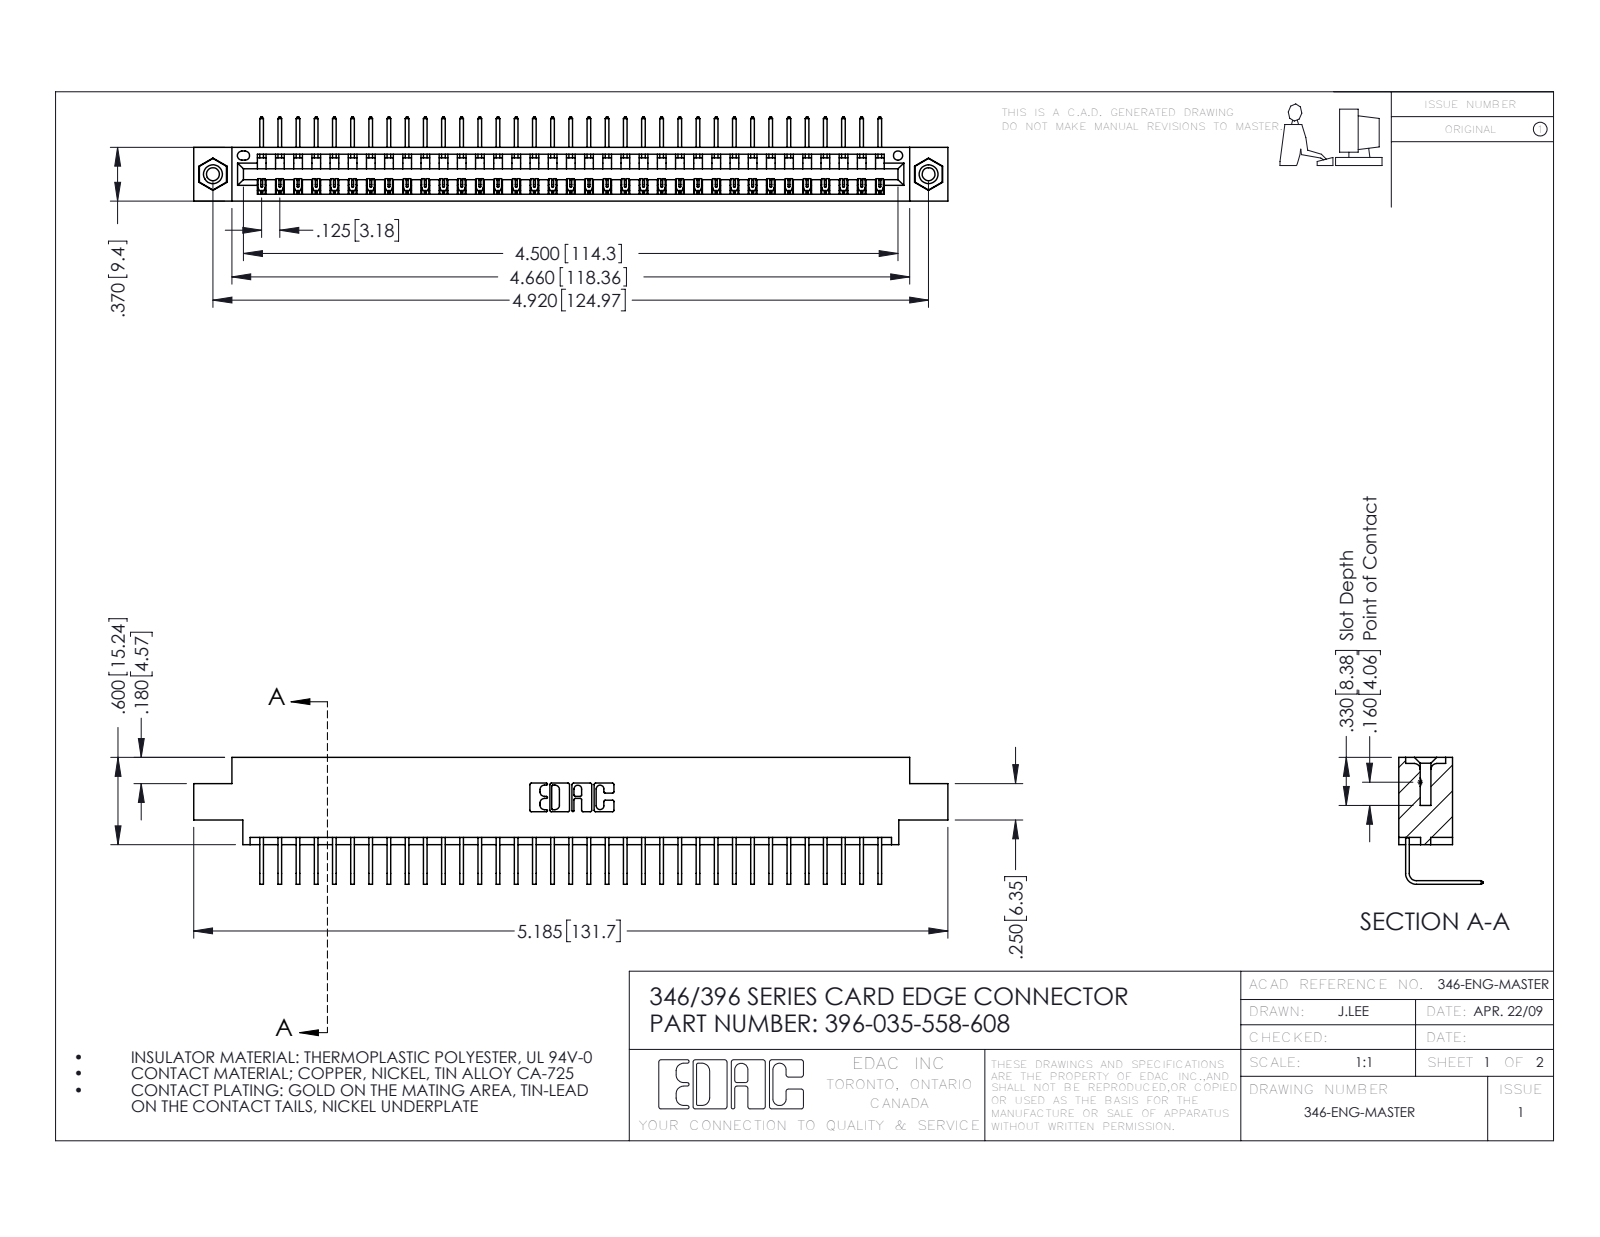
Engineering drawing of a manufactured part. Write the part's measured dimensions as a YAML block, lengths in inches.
part_name: "345-250-001_345-250-003-102; 396-035-558-608; 346 Part_0.170 Offset - 0.156 Dia-TI; 345-292-001_558 Tail - 2"
step_written_by: "SolidWorks 2016 (CONFIG_CONTROL_DESIGN)"
units: inches
bodies: {solids: 38, faces: 2286, planar: 1582, cylindrical: 688, other: 16}
overall_size: [5.185, 0.873, 0.58]
volume: 0.764
surface_area: 25.49
round_holes:
  - {diameter: 0.089, count: 2}
  - {diameter: 0.125, count: 2}
  - {diameter: 0.156, count: 2}
  - {diameter: 0.064, count: 1}
round_bosses_or_shafts:
  - {diameter: 0.155, count: 2}
partial_cylinders:
  - {radius: 0.006, count: 70}
  - {radius: 0.01, count: 22}
  - {radius: 0.007, count: 6}
  - {radius: 0.031, count: 6}
  - {radius: 0.026, count: 3}
  - {radius: 0.031, count: 2}
  - {radius: 0.04, count: 2}
  - {radius: 0.014, count: 1}
face_to_face_distances: [0.322, 0.048, 0.37, 0.25, 0.298, 0.025, 0.072, 0.222, 0.148, 0.1]
hole_center_spacings: [0.246, 4.711, 4.92]
